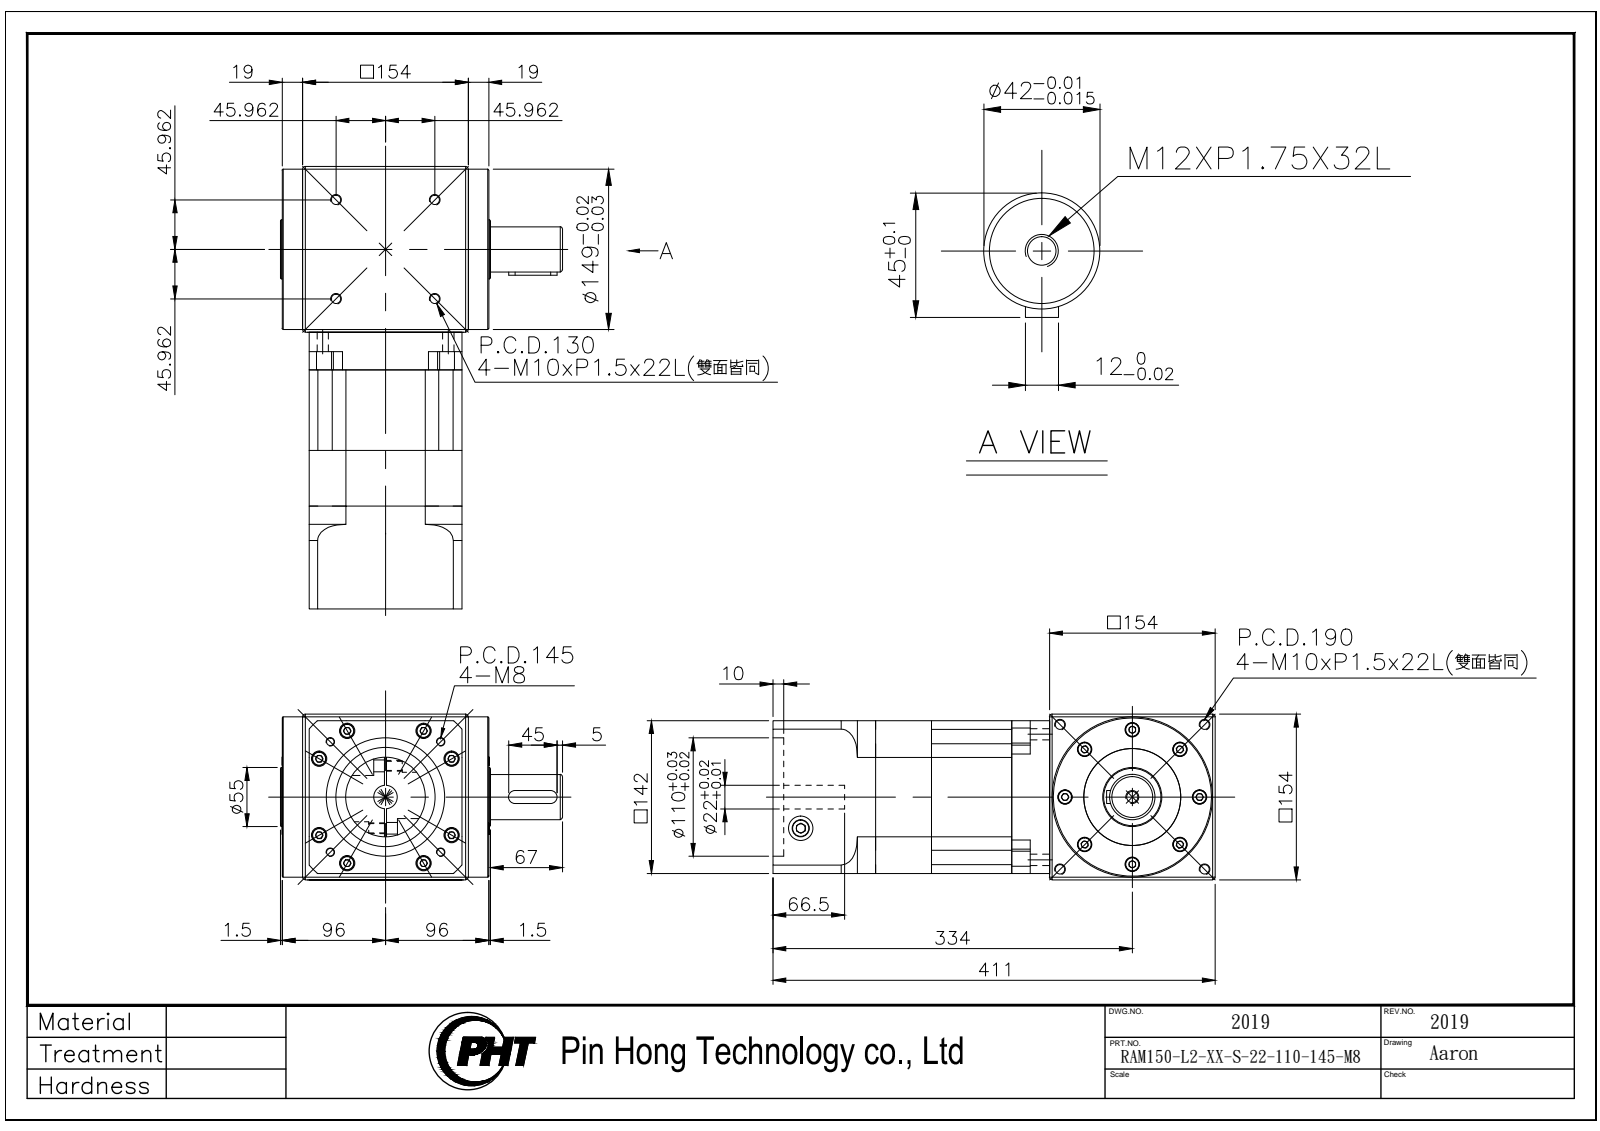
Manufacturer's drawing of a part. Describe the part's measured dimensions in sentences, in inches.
The part is named "RAM150-L2-XX-S-22-110-145-M8_2019". Its 3-D file was written by "SolidWorks 2016 (AUTOMOTIVE_DESIGN)". It is 6 solids with 892 faces: 435 planar, 297 cylindrical and 160 other. Overall it measures 16.181 by 10.315 by 6.063 inches. Its volume is 541.3 cubic inches and its surface area 898.5 square inches. Round holes: 12 of diameter 0.335, 8 of diameter 0.354, 8 of diameter 0.433, 8 of diameter 0.551, 8 of diameter 0.689, 4 of diameter 0.268, 4 of diameter 0.413, 2 of diameter 0.886, 1 of diameter 0.161, 1 of diameter 0.402, 1 of diameter 0.866, 1 of diameter 3.622. Round bosses or shafts: 12 of diameter 0.63, 8 of diameter 0.512, 1 of diameter 5.866, 1 of diameter 5.118, 1 of diameter 3.543, 1 of diameter 2.913, 1 of diameter 2.165, 1 of diameter 1.654. Partial cylindrical surfaces (rounded edges, fillets, slot ends): 4 of radius 0.394, 2 of radius 0.236, 1 of radius 3.15, 1 of radius 3.74, 1 of radius 4.228. The main face-to-face distances are 0.236, 5.827, 6.063, 5.591, 2.039, 4.98, 2.941, 1.378, 6.358, 4.319. The hole center spacings are 2.795, 0.737, 0.74, 0.908, 1.883, 2.651, 3.265, 3.44.
